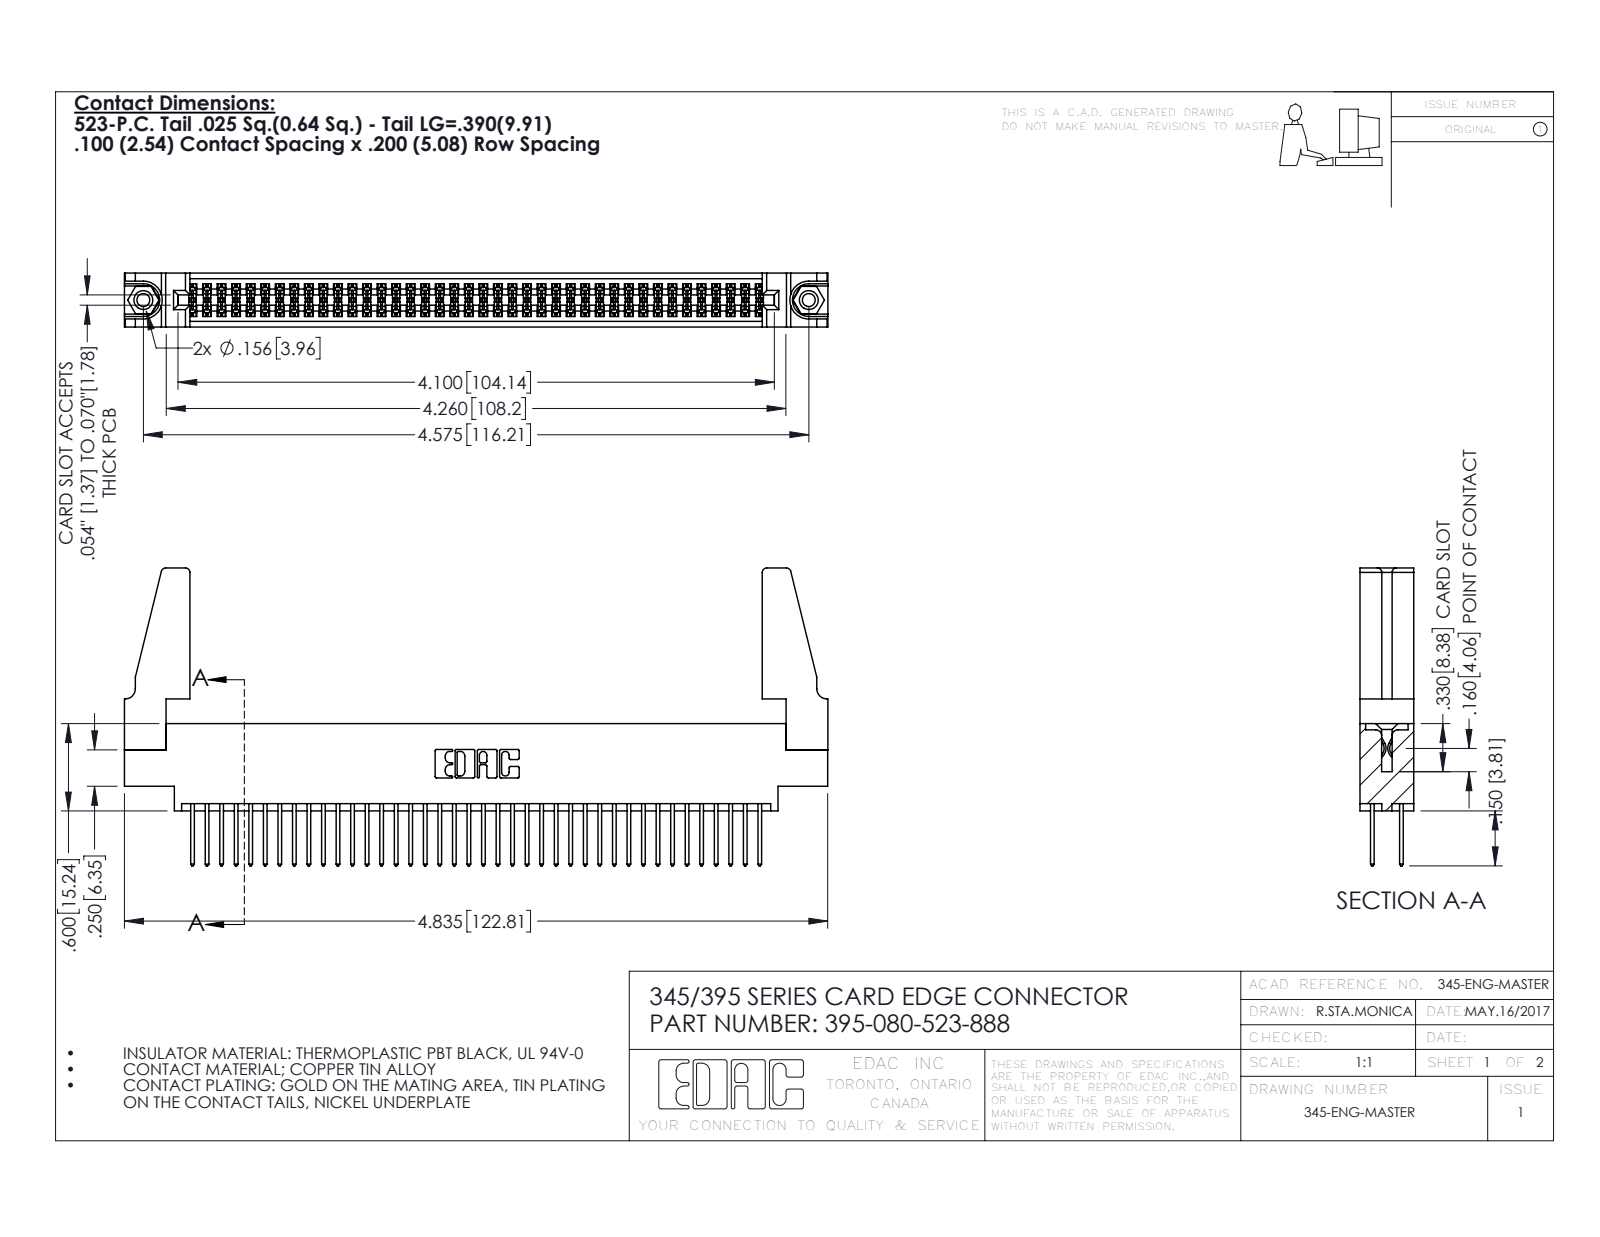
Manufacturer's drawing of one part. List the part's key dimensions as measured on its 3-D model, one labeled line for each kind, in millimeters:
Part name (STEP PRODUCT): 395-080-523-888; 345 Part_0.170 Offset - 0.156 Dia-TH; 345-220-078_345-220-088; 345-292-001_345-293-123 (+1 more)
STEP written by: SolidWorks 2016 (CONFIG_CONTROL_DESIGN)
Units: millimetres
Bodies: 85 solids, 4254 faces (2796 planar, 1442 cylindrical, 16 other)
Overall size (bounding box): 122.8 × 52 × 9.4
Volume: 15 200 mm³ · Surface area: 21 650 mm²
Round holes (diameter × count): ⌀2.3 ×2, ⌀3.2 ×2, ⌀4 ×2, ⌀1.6 ×1
Round bosses / shafts (diameter × count): ⌀3.9 ×2
Partial cylindrical surfaces — rounded edges, fillets, slot ends (radius × count): R0.2 ×120, R0.3 ×80, R0.3 ×22, R0.8 ×8, R0.2 ×6, R0.8 ×6, R0.7 ×3, R0.4 ×2
Main face-to-face distances: 1.8, 7.6, 9.4, 5.1, 2.5, 6.9, 0.6, 5.7, 4.4, 3.8
Hole centre spacings: 6.9, 110.2, 116.2
